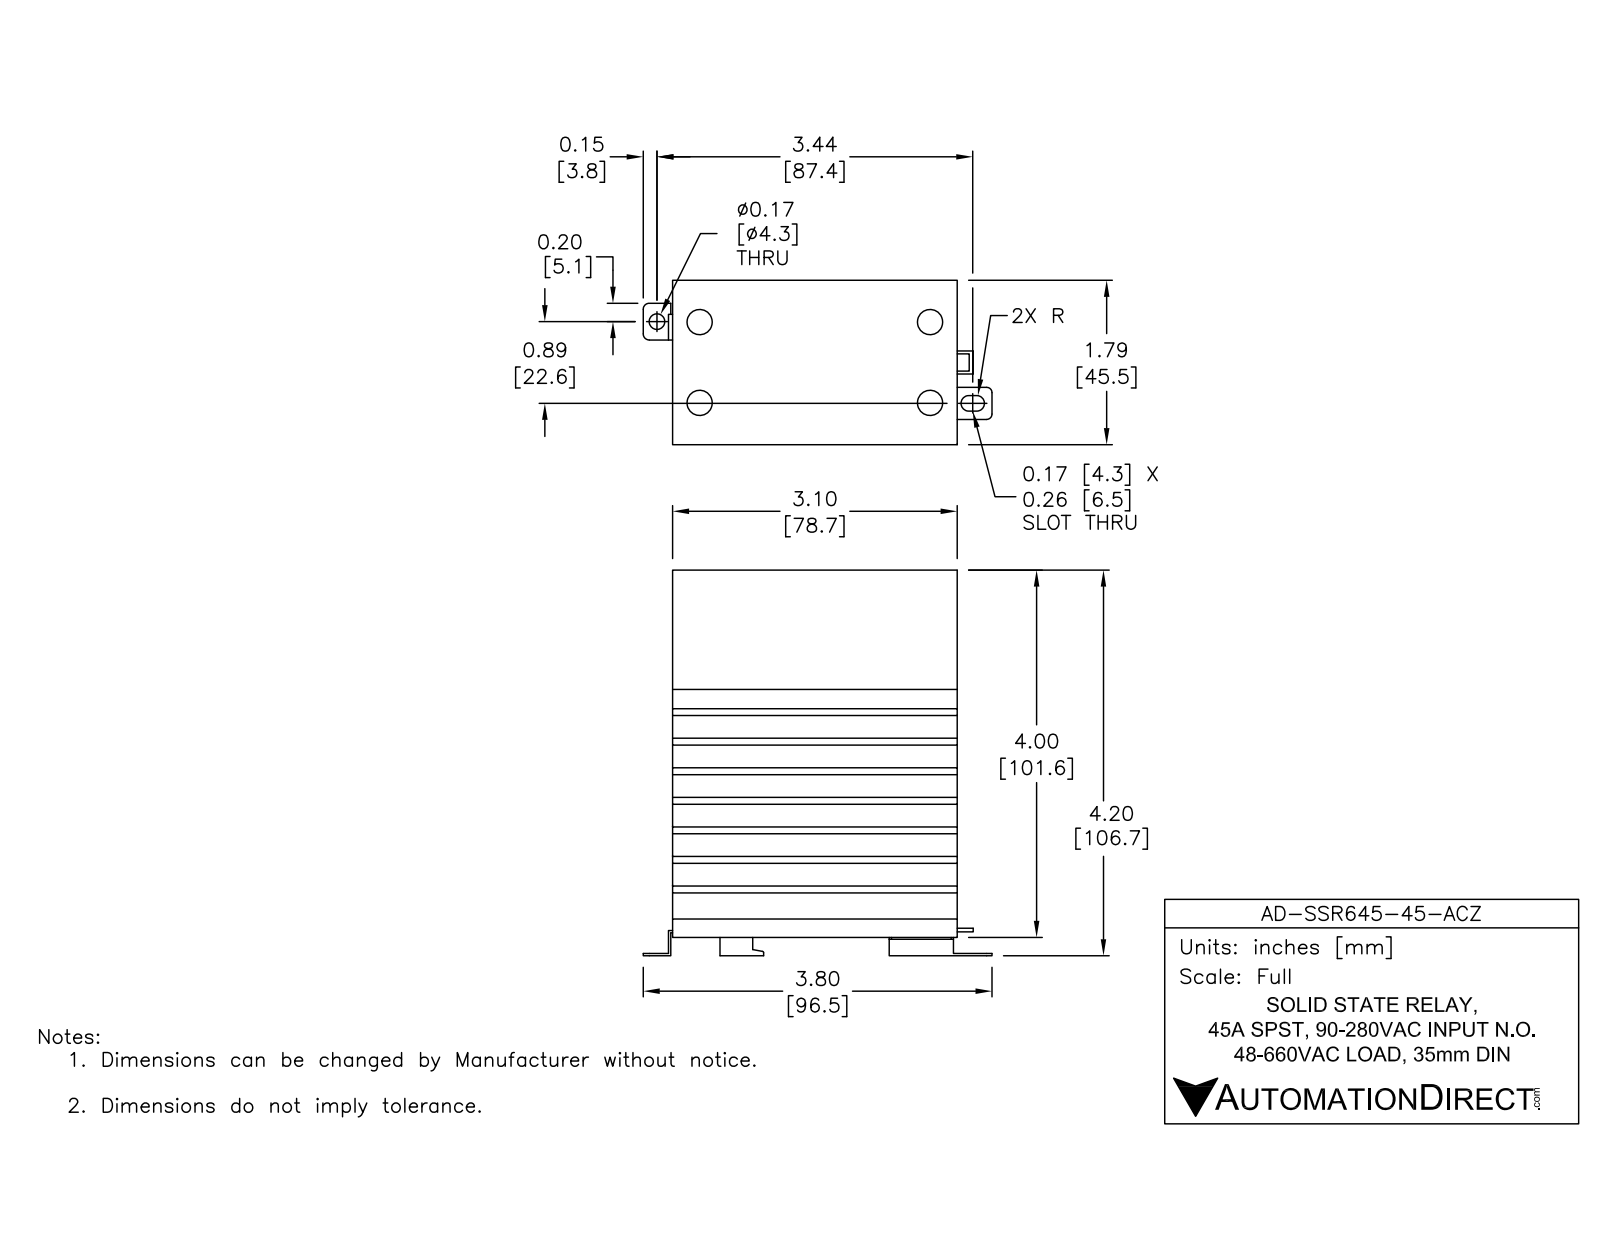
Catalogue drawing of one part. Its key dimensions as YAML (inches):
part_name: "AD-SSR645-45-ACZ"
step_written_by: "SolidWorks 2014 (AUTOMOTIVE_DESIGN)"
units: inches
bodies: {solids: 1, faces: 171, planar: 151, cylindrical: 20, other: 0}
overall_size: [4.2, 3.8, 1.79]
volume: 12.46
surface_area: 125.1
round_holes:
  - {diameter: 0.275, count: 2}
  - {diameter: 0.275, count: 2}
  - {diameter: 0.17, count: 1}
partial_cylinders:
  - {radius: 0.05, count: 2}
  - {radius: 0.058, count: 2}
  - {radius: 0.067, count: 2}
  - {radius: 0.085, count: 2}
  - {radius: 0.015, count: 1}
face_to_face_distances: [0.644, 0.322, 0.966, 0.397, 0.322, 0.247, 1.609, 0.075, 0.569, 0.075]
hole_center_spacings: [0.88, 2.51, 2.66, 0.465, 1, 2.975, 3.104]
